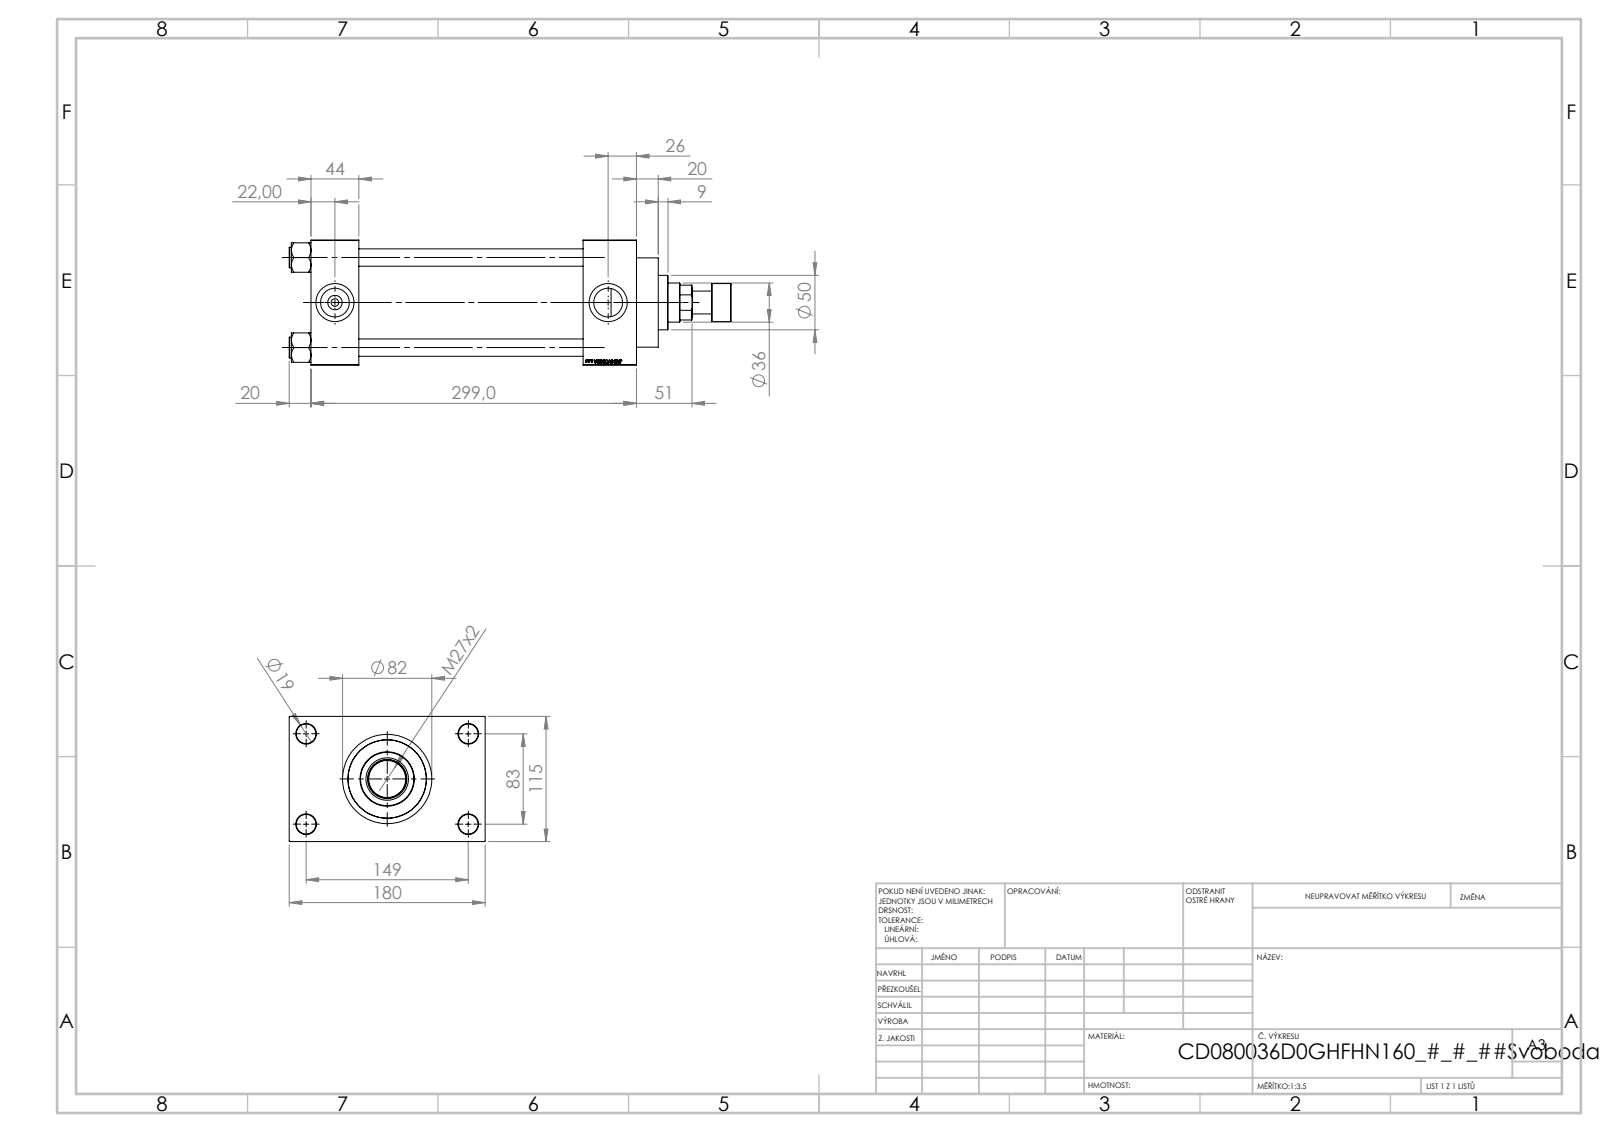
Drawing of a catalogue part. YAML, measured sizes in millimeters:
part_name: "V215CD_D_Body; V215CD_NUT_M5_D; V215CD_VCP_D; V215CR_ROD_END_F (+2 more)"
step_written_by: "SolidWorks 2019 (CONFIG_CONTROL_DESIGN)"
units: millimeters
bodies: {solids: 12, faces: 1165, planar: 549, cylindrical: 92, other: 524}
overall_size: [406, 180, 115]
volume: 2368000
surface_area: 419154
round_holes:
  - {diameter: 16, count: 4}
  - {diameter: 18, count: 4}
  - {diameter: 7, count: 2}
  - {diameter: 26.44, count: 2}
  - {diameter: 35, count: 2}
  - {diameter: 25.5, count: 1}
  - {diameter: 36, count: 1}
  - {diameter: 39, count: 1}
  - {diameter: 61, count: 1}
  - {diameter: 72, count: 1}
  - {diameter: 80, count: 1}
round_bosses_or_shafts:
  - {diameter: 19, count: 4}
  - {diameter: 86, count: 1}
  - {diameter: 82, count: 1}
  - {diameter: 50, count: 1}
  - {diameter: 35, count: 1}
  - {diameter: 21, count: 1}
face_to_face_distances: [115, 206, 49, 255, 44, 250, 299, 32.5, 147.5, 180]
hole_center_spacings: [33.15, 58.48, 82.7, 85.28, 89.24, 115.85, 142.43, 83]
